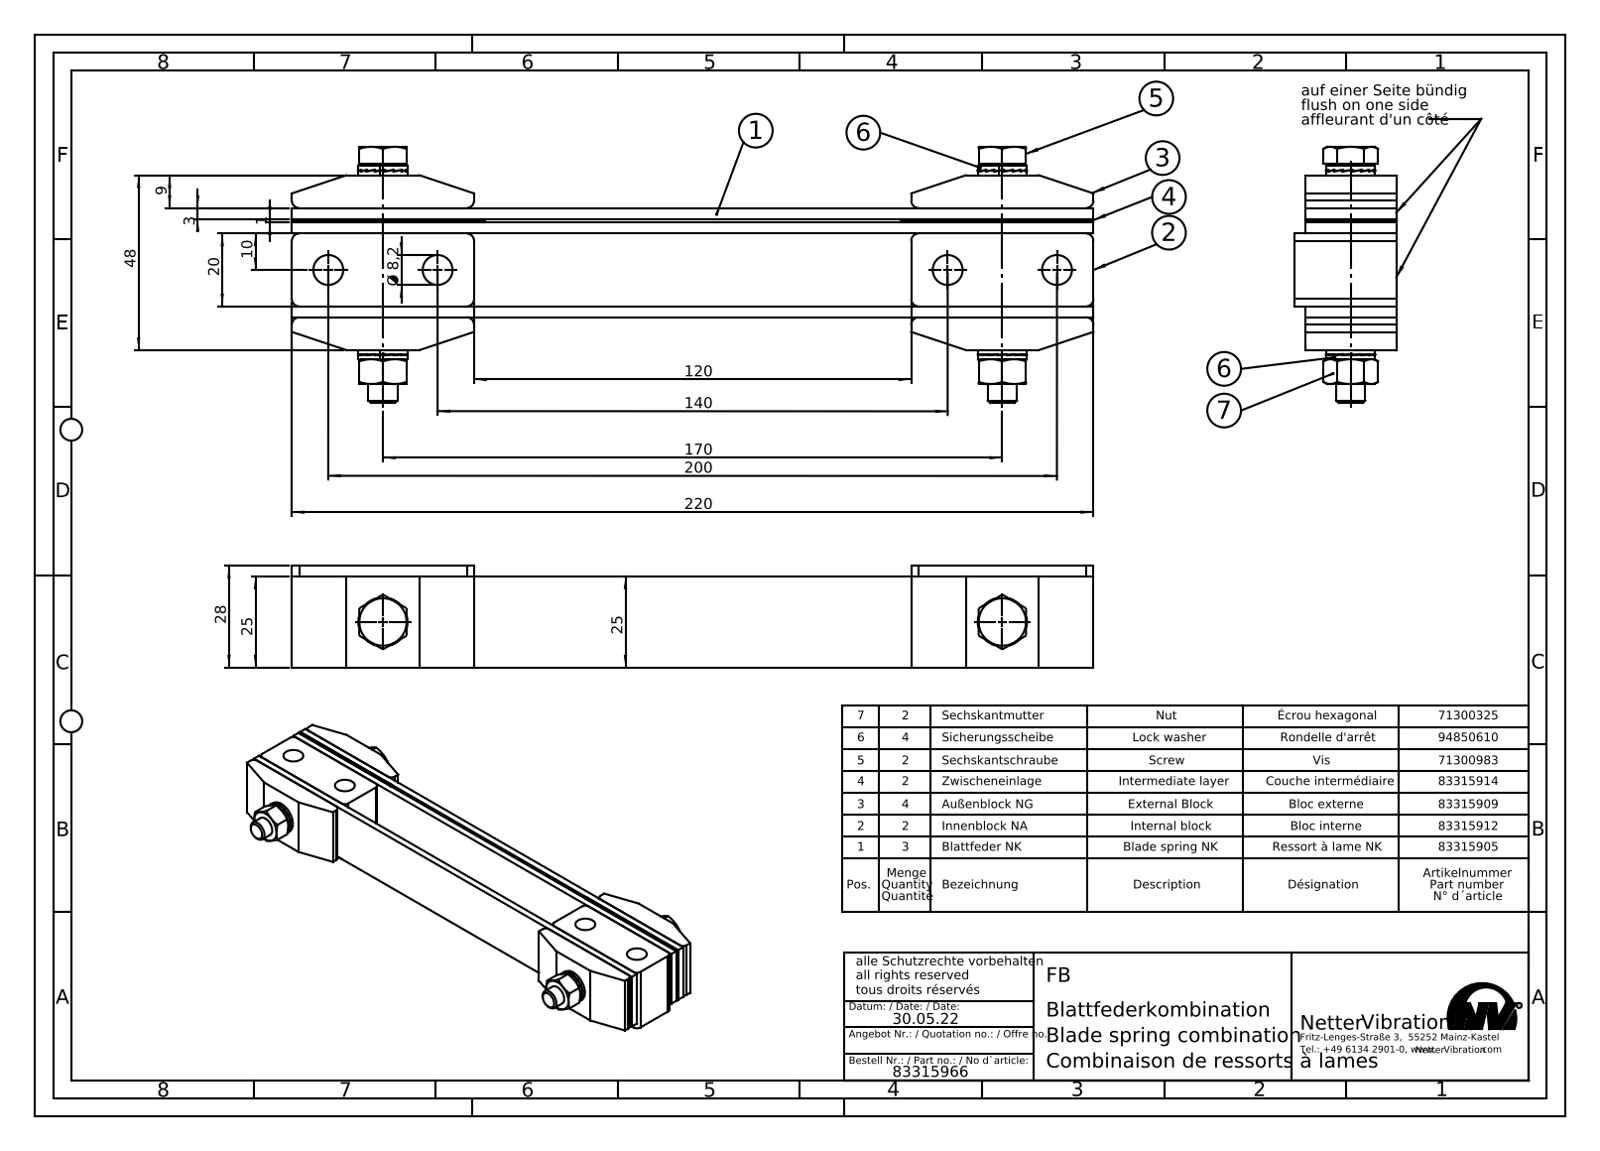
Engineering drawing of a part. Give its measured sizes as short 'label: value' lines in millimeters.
name: Blattfederkombination FB # 83315966
written by: SolidWorks 2015 (AUTOMOTIVE_DESIGN)
unit: mm
bodies: 19 solids, 720 faces (576 planar, 92 cylindrical, 52 other)
size: 220 × 70.3 × 28
volume: 144 592 mm³; area: 78 976 mm²
holes: 6× ⌀8.2, 2× ⌀6.8, 2× ⌀8, 2× ⌀8.5, 2× ⌀8.7
bosses: 2× ⌀13.5, 2× ⌀13
rounds: 16× R2
face distances: 3, 4, 23, 27, 1, 24, 20, 7, 30, 26
hole spacings: 170, 30, 140, 200
